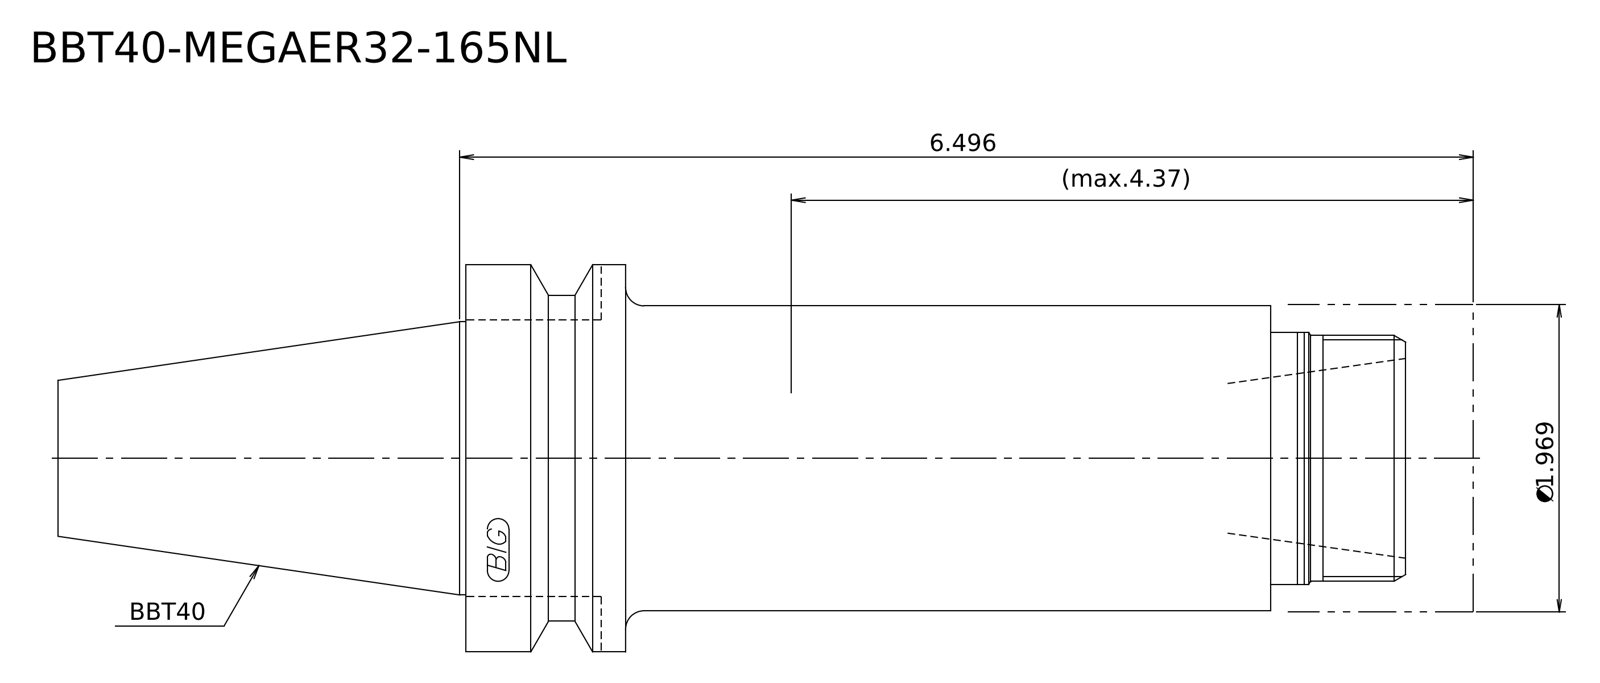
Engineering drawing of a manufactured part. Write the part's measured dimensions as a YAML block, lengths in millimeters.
step_written_by: "Kubotek KeyCreator 2011 V10.0.2 (22737) (automotive_design)"
units: millimeters
bodies: {solids: 2, faces: 21, planar: 6, cylindrical: 8, other: 7}
overall_size: [230.4, 63, 63]
volume: 430976
surface_area: 45972
round_bosses_or_shafts:
  - {diameter: 63, count: 1}
  - {diameter: 53, count: 1}
  - {diameter: 50, count: 1}
  - {diameter: 49.6, count: 1}
  - {diameter: 44.45, count: 1}
  - {diameter: 41, count: 1}
  - {diameter: 40, count: 1}
face_to_face_distances: [30.2, 164, 133.8, 11, 19.2, 153, 33, 22, 2.8, 131]
